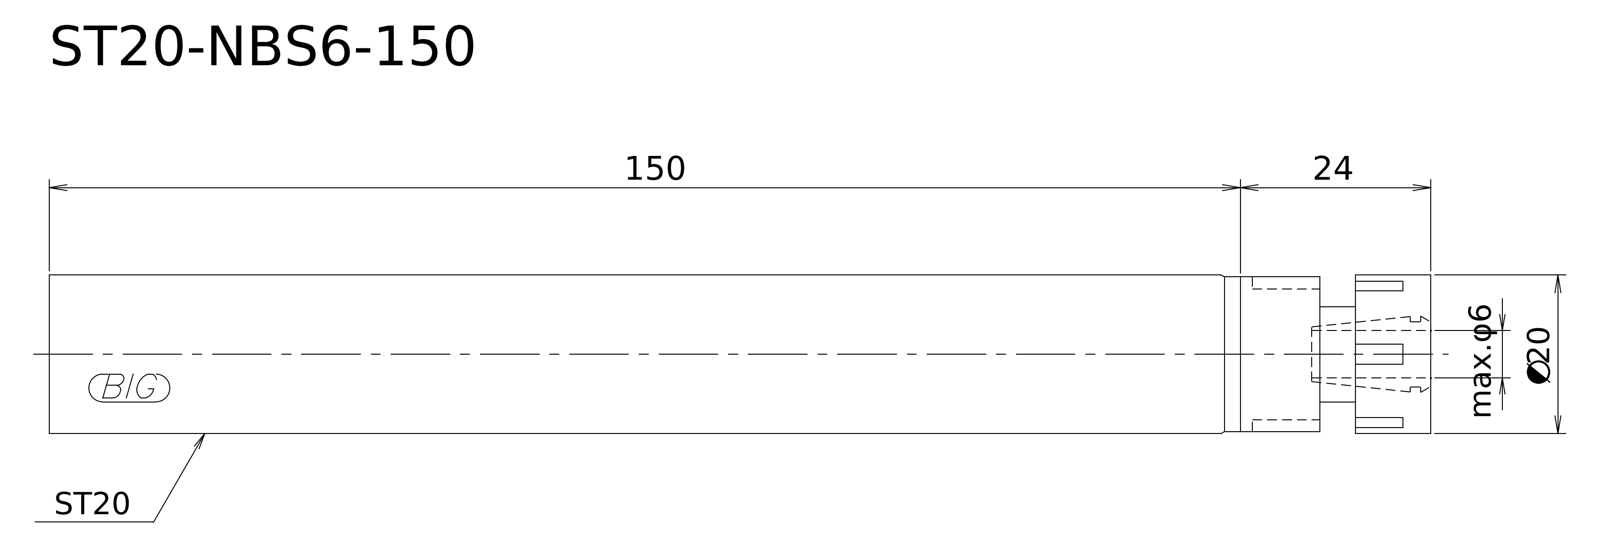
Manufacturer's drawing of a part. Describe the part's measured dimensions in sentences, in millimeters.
Its 3-D file was written by "Kubotek KeyCreator V8.5.1 (14335) (CONFIG_CONTROL_DESIGN)". It is 1 solid with 9 faces: 5 planar, 4 cylindrical and 0 other. Overall it measures 174 by 20 by 20 millimeters. Its volume is 53 572 cubic millimeters and its surface area 11 831 square millimeters. Round bosses or shafts: 1 of diameter 20, 1 of diameter 19.5, 1 of diameter 12. The main face-to-face distances are 174, 9.5, 164.5, 14, 4.5, 160, 26.05, 16.55, 12.05, 147.95.
